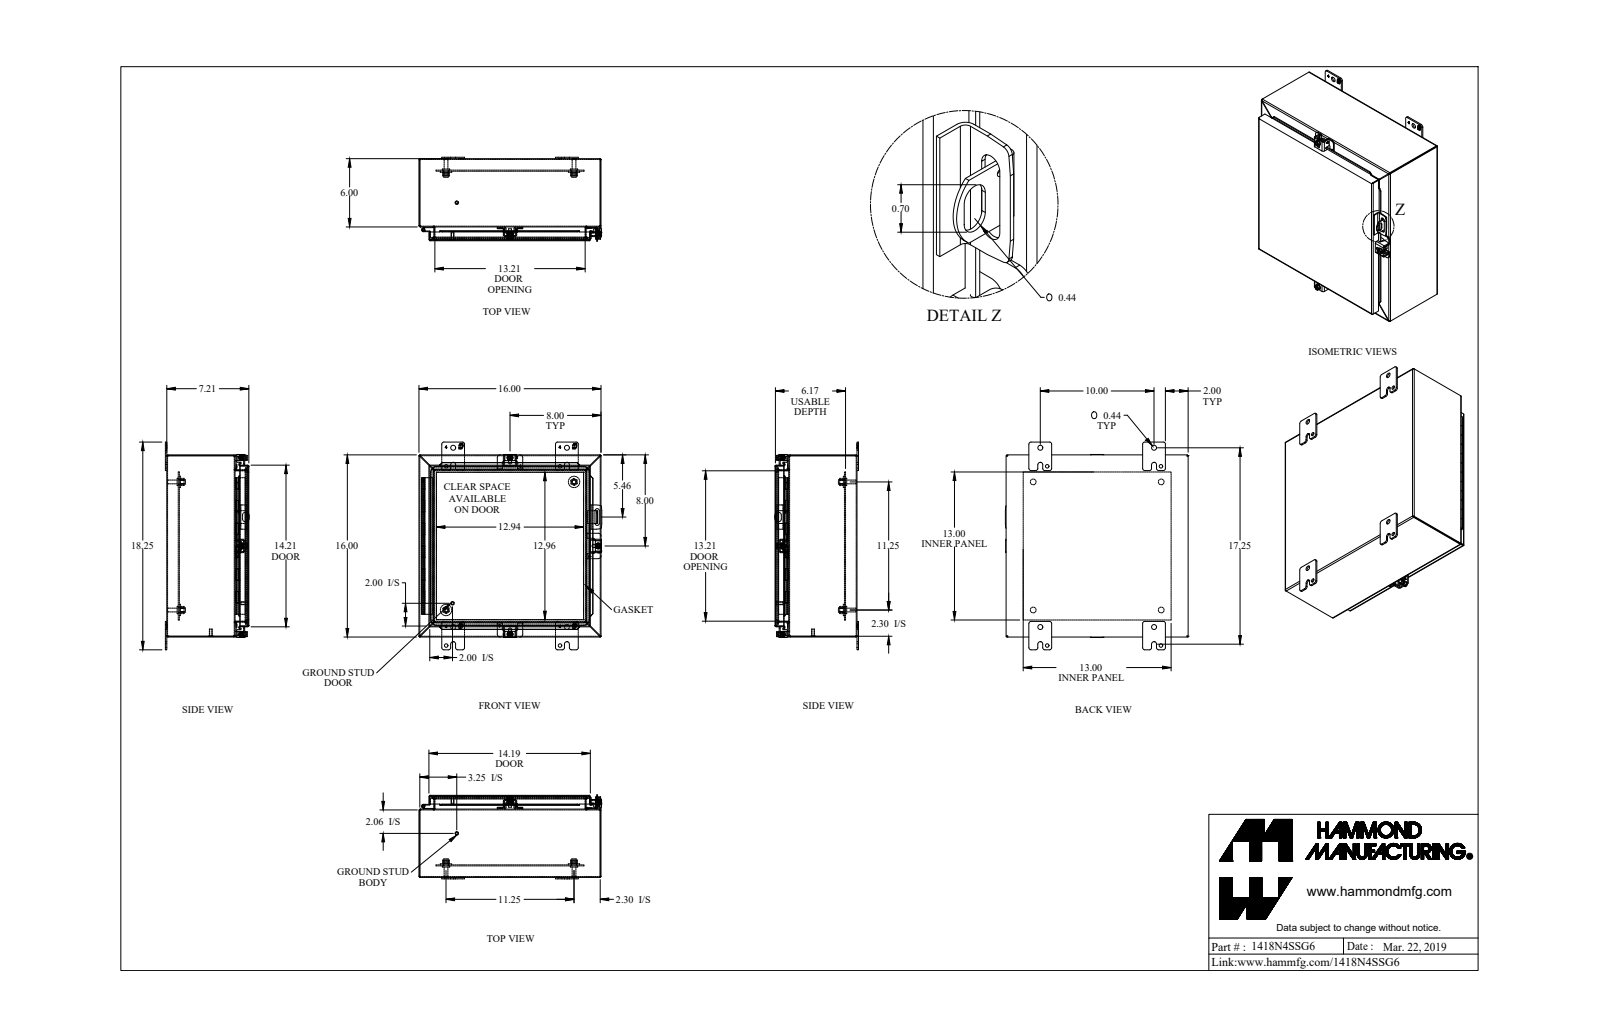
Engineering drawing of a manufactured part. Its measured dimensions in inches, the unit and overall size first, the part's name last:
Units: inches
Overall size (bounding box): 18.25 × 16.063 × 7.375
Round holes (diameter × count): ⌀0.313 ×4, ⌀0.437 ×4, ⌀0.5 ×4, ⌀0.213 ×3, ⌀0.265 ×3, ⌀0.375 ×3, ⌀0.307 ×2, ⌀0.445 ×2, ⌀0.125 ×1, ⌀0.187 ×1
Round bosses / shafts (diameter × count): ⌀0.65 ×4, ⌀0.375 ×4, ⌀0.332 ×4, ⌀0.5 ×3, ⌀0.39 ×3, ⌀0.244 ×3, ⌀1 ×2, ⌀0.313 ×2
Partial cylindrical surfaces — rounded edges, fillets, slot ends (radius × count): R0.188 ×26, R0.036 ×24, R0.108 ×24, R0.25 ×16, R0.048 ×15, R0.143 ×15, R0.045 ×8, R0.125 ×8
Main face-to-face distances: 0.072, 15.928, 0.072, 7.066, 7.138, 7.138, 7.21, 0.937, 15.856, 16
Hole centre spacings: 14.51, 6.013, 11.25, 1.735, 10, 15.75, 18.656, 3.064
Volume: 101.1 in³ · Surface area: 2 679 in²
Bodies: 35 solids, 1283 faces (801 planar, 392 cylindrical, 90 other)
Part name (STEP PRODUCT): 1418N4SSG6_Default
STEP written by: SolidWorks 2019 (CONFIG_CONTROL_DESIGN)
